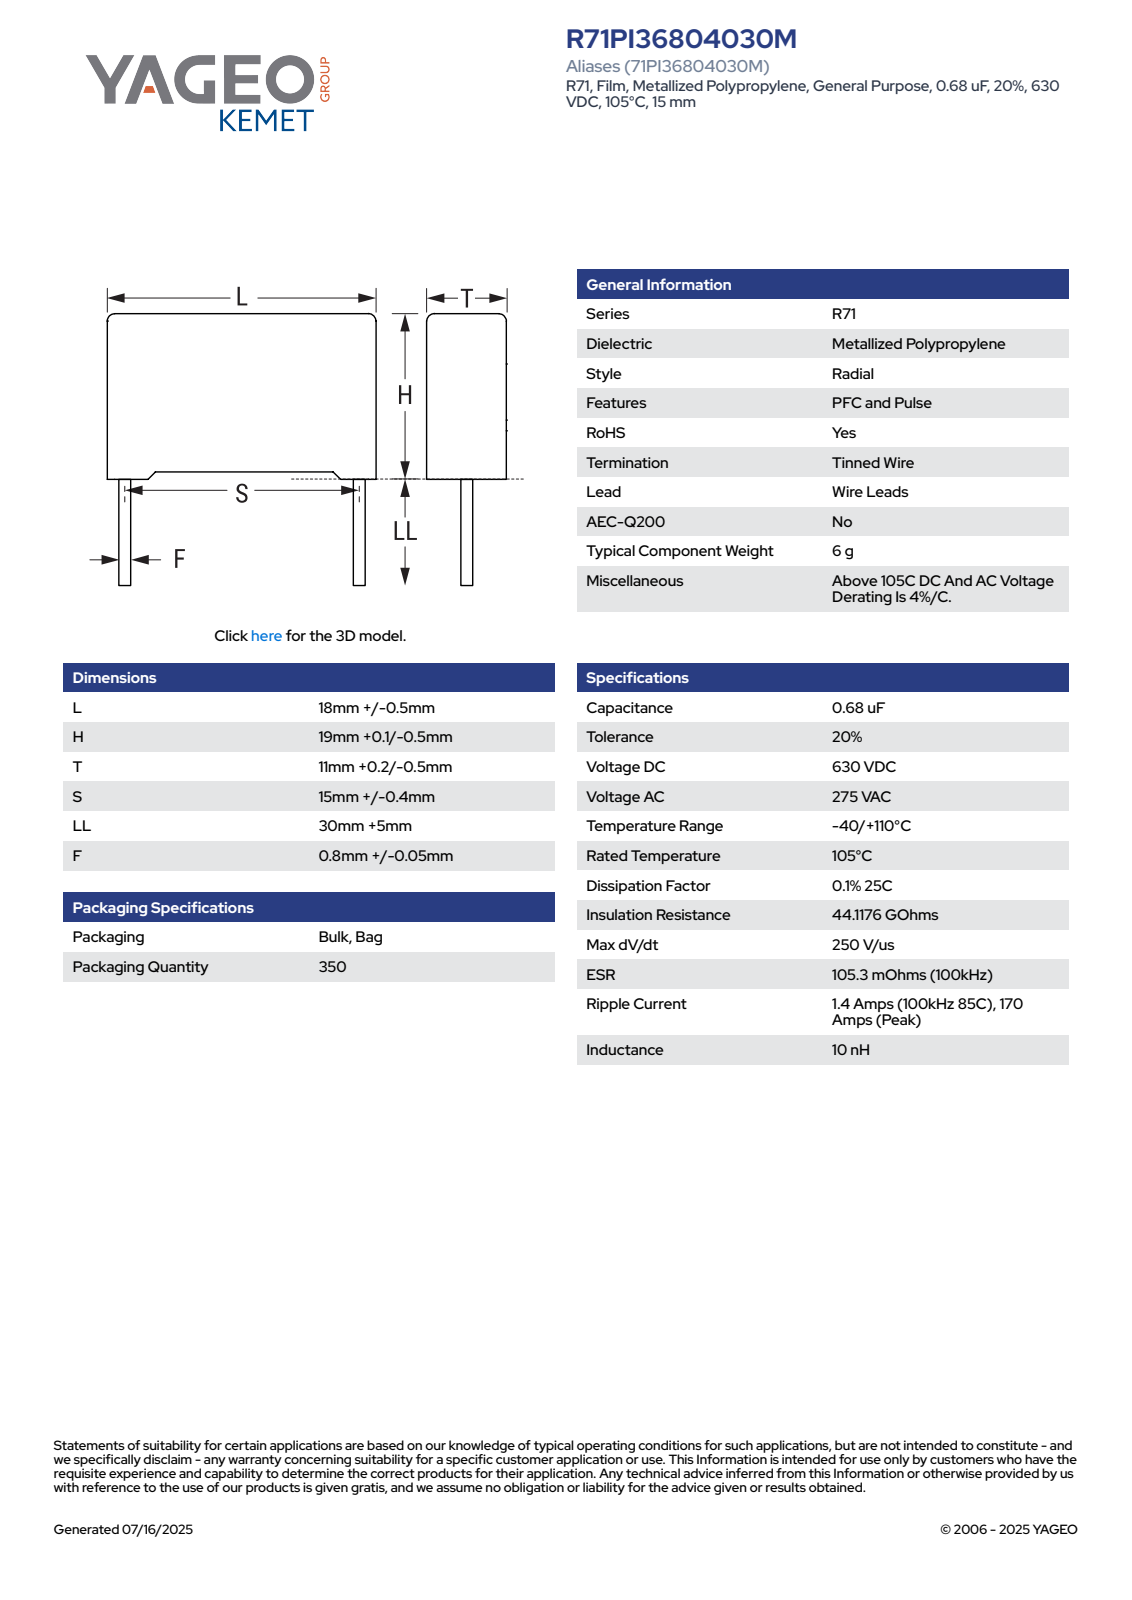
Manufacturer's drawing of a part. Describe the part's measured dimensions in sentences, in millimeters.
The part is named "CFR_RB2_18X19X11_L18.5H19.1T11.2S15LL35F0.85". Its 3-D file was written by "SolidWorks 2021 (AUTOMOTIVE_DESIGN)". It is 4 solids with 85 faces: 77 planar, 8 cylindrical and 0 other. Overall it measures 54.1 by 18.5 by 11.21 millimeters. Its volume is 3 857 cubic millimeters and its surface area 1 764 square millimeters. Round bosses or shafts: 2 of diameter 0.85. Partial cylindrical surfaces (rounded edges, fillets, slot ends): 4 of radius 0.5. The main face-to-face distances are 11.2, 18.5, 18.35, 0.62, 0.75, 19.1, 17.88, 0.66, 18.44, 10.58.
